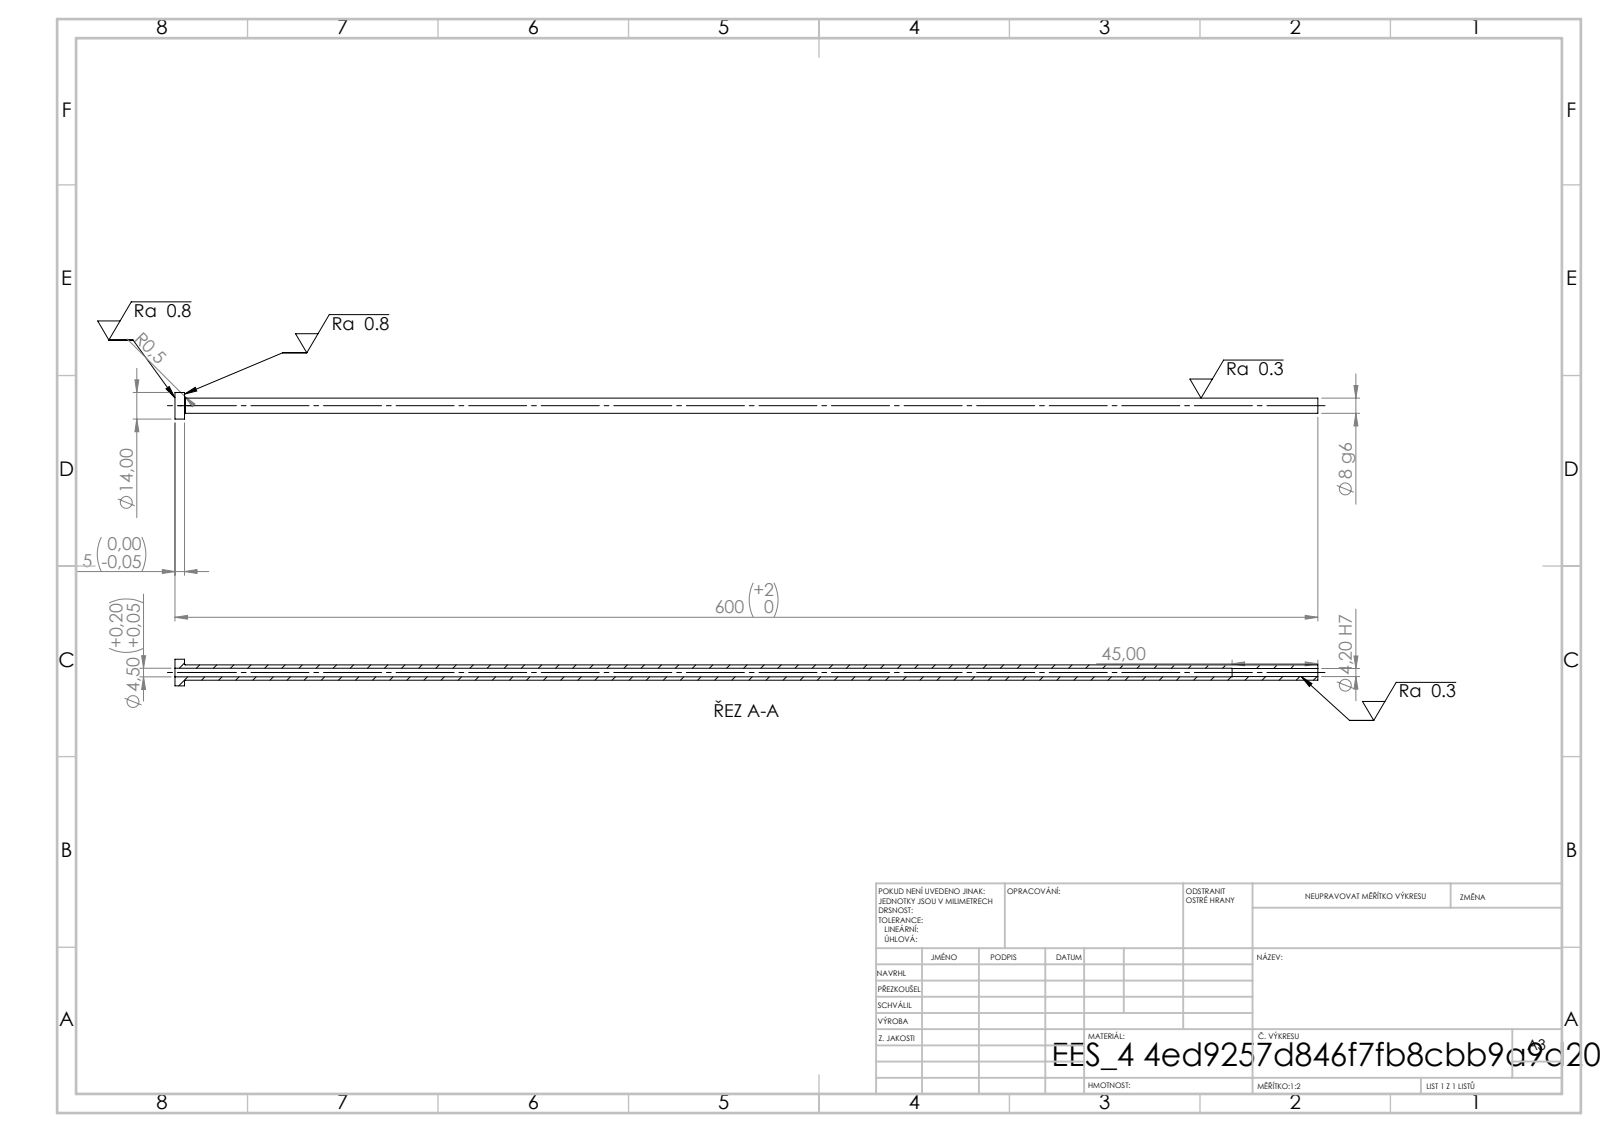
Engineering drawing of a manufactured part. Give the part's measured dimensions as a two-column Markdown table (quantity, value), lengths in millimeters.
| quantity | value |
| --- | --- |
| STEP written by | SolidWorks 2019 (CONFIG_CONTROL_DESIGN) |
| units | millimeters |
| bodies | 1 solid, 14 faces (4 planar, 8 cylindrical, 2 other) |
| overall size | 600 × 14 × 14 |
| volume | 21 229 mm³ |
| surface area | 23 889 mm² |
| round holes (diameter × count) | 4.2 × 1, 4.5 × 1 |
| round bosses / shafts (diameter × count) | 14 × 1, 8 × 1 |
| main face-to-face distances | 5, 600, 595, 555, 550, 45 |
